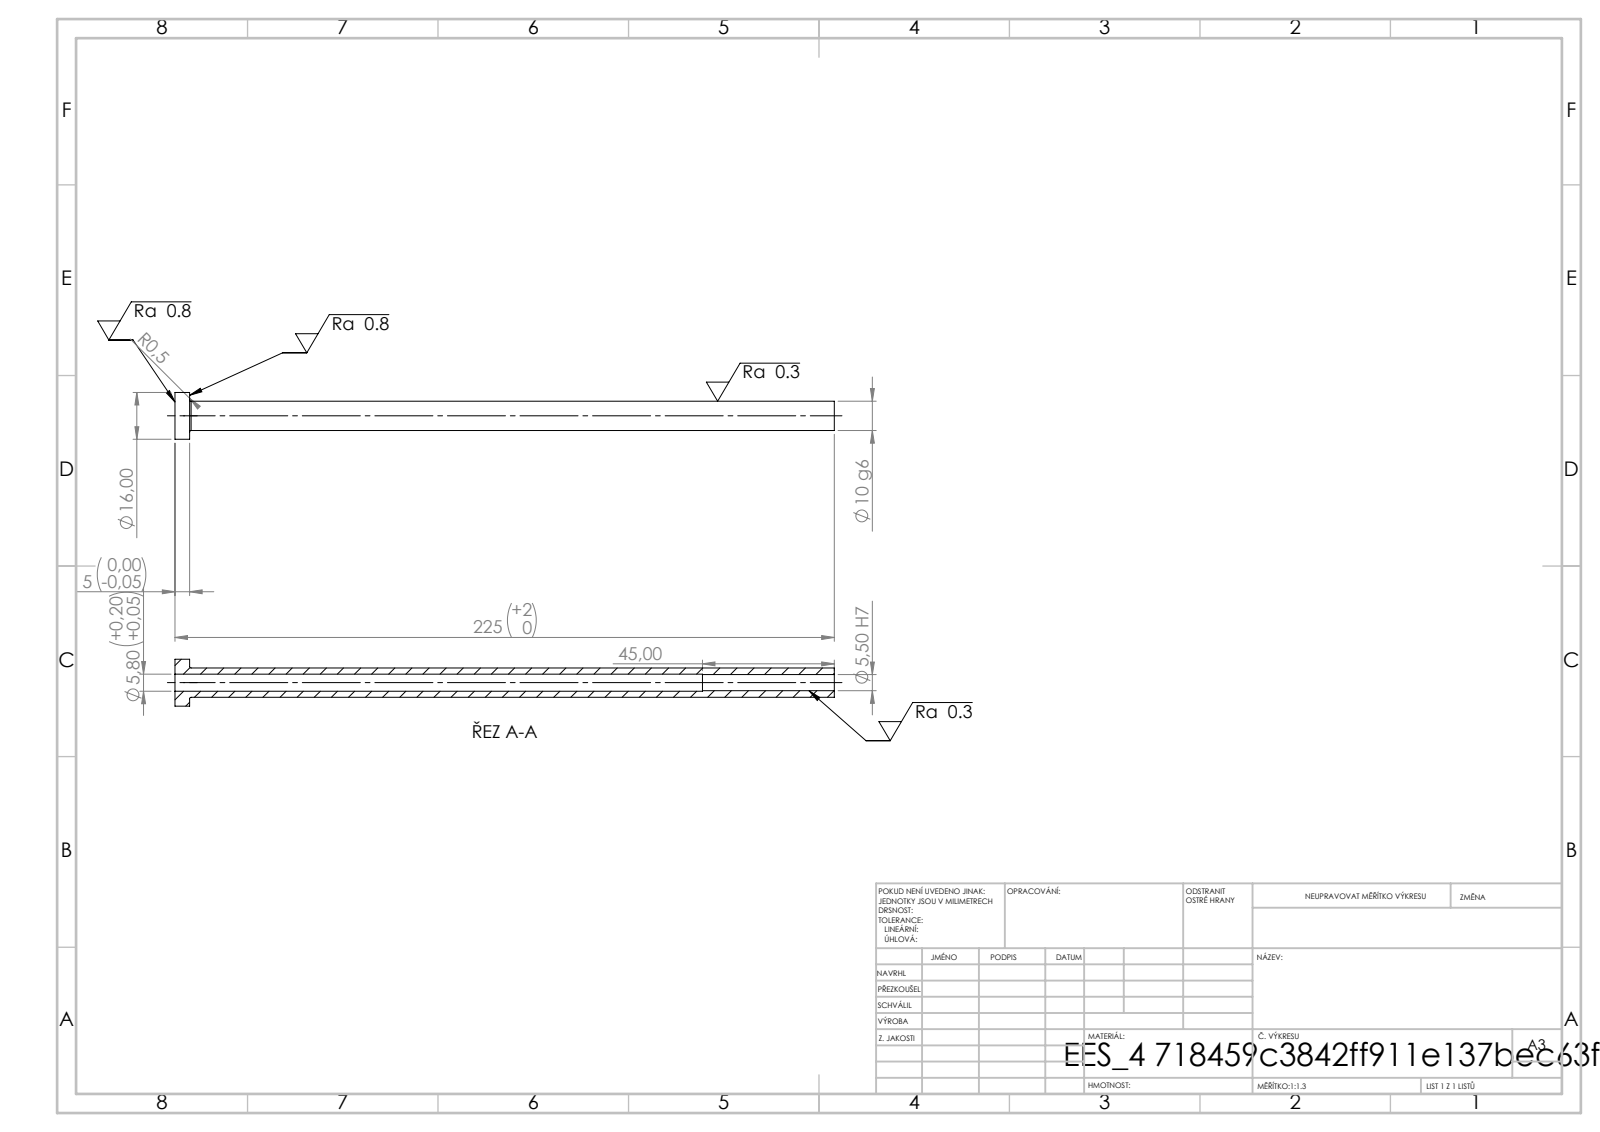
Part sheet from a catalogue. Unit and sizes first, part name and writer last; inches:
Units: inches
Overall size (bounding box): 8.858 × 0.63 × 0.63
Round holes (diameter × count): ⌀0.217 ×1, ⌀0.228 ×1
Round bosses / shafts (diameter × count): ⌀0.63 ×1, ⌀0.394 ×1
Main face-to-face distances: 0.197, 8.858, 8.661, 7.087, 6.89, 1.772
Volume: 0.76 in³ · Surface area: 17.93 in²
Bodies: 1 solid, 14 faces (4 planar, 8 cylindrical, 2 other)
STEP written by: SolidWorks 2019 (CONFIG_CONTROL_DESIGN)
